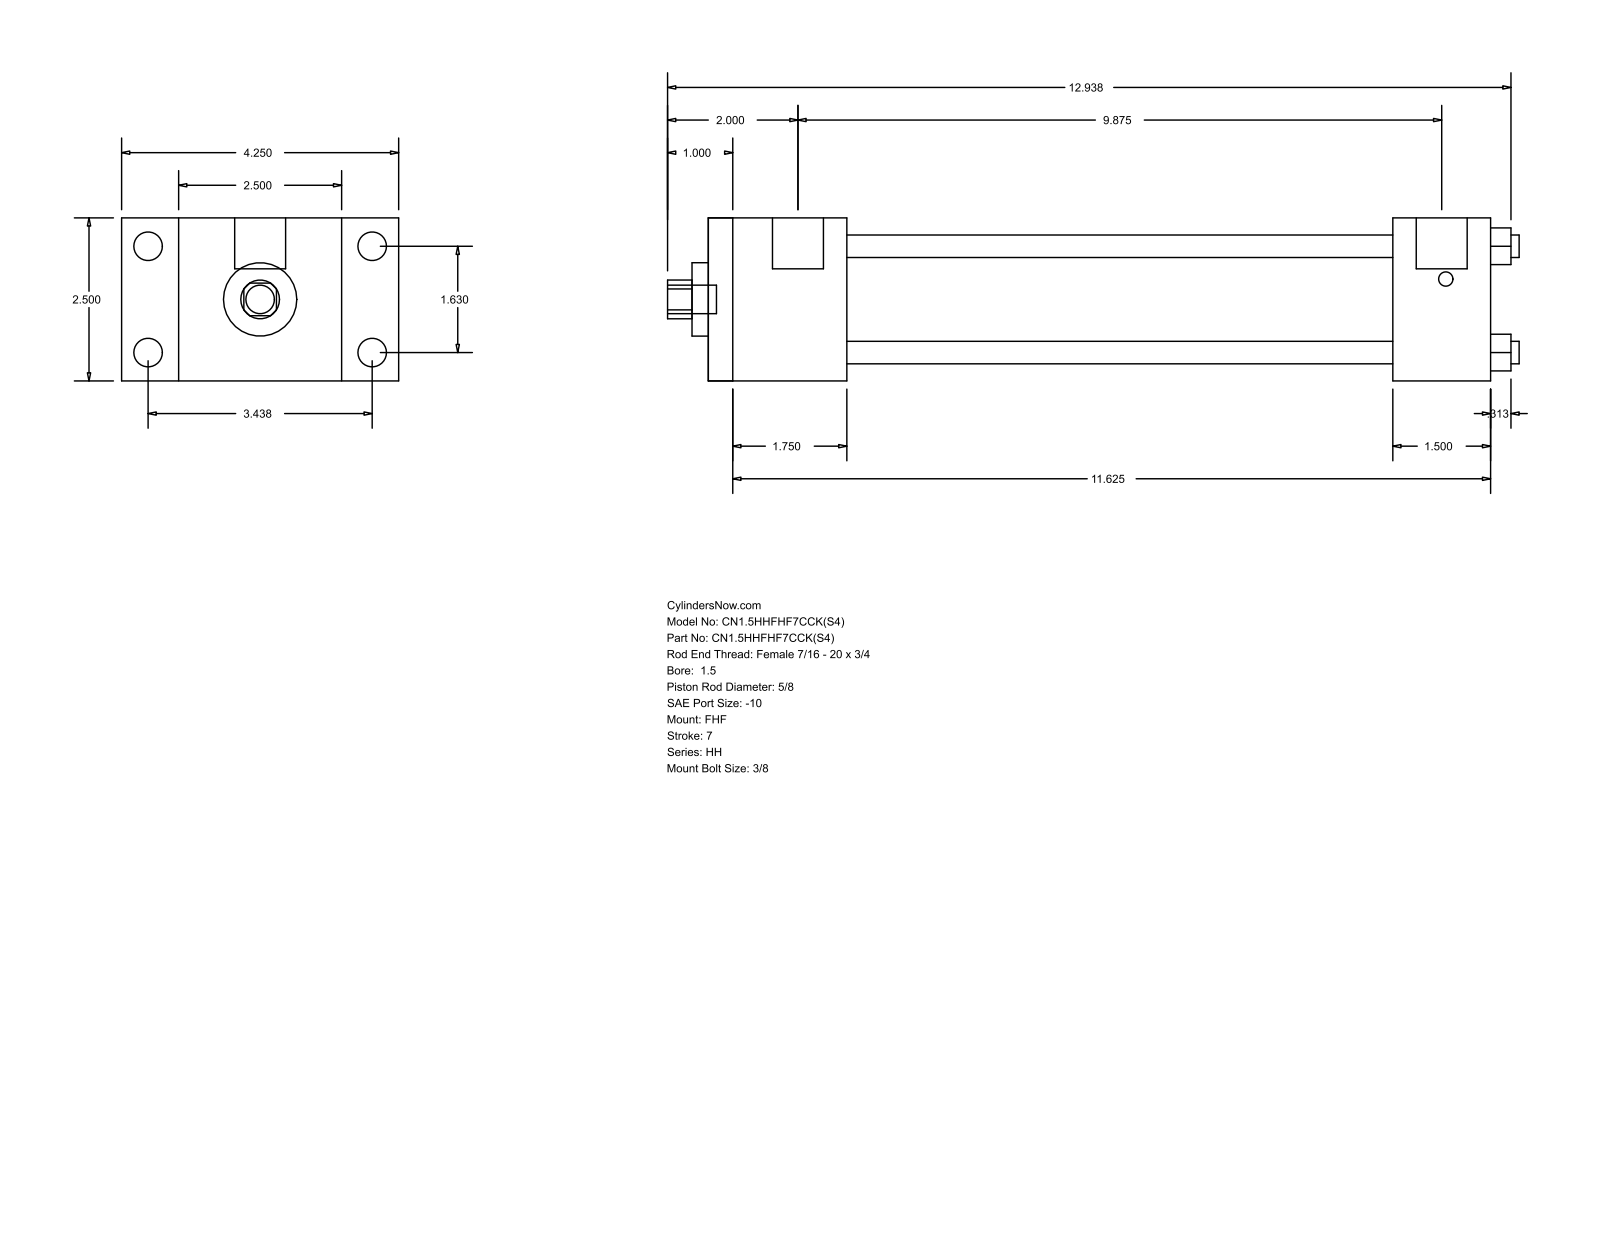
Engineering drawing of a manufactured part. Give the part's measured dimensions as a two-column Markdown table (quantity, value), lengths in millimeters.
| quantity | value |
| --- | --- |
| part name | HH_FHF__0150_0.625 |
| STEP written by | GSSL Pune (CONFIG_CONTROL_DESIGN) |
| units | millimeters |
| bodies | 0 solids, 88 faces (60 planar, 28 cylindrical, 0 other) |
| overall size | 331.79 × 107.95 × 63.5 |
| round holes (diameter × count) | 8.76 × 4, 15.88 × 1, 28.57 × 1, 44.45 × 1 |
| round bosses / shafts (diameter × count) | 11.13 × 4, 5.56 × 4, 19.84 × 2, 11.11 × 1 |
| partial cylindrical surfaces (radius × count) | 7.54 × 1 |
| main face-to-face distances | 63.5, 22.23, 85.73, 53.97, 107.96, 304.8, 250.83, 266.69, 212.72, 38.11 |
| hole center spacings | 29.27, 41.4, 58.55 |
